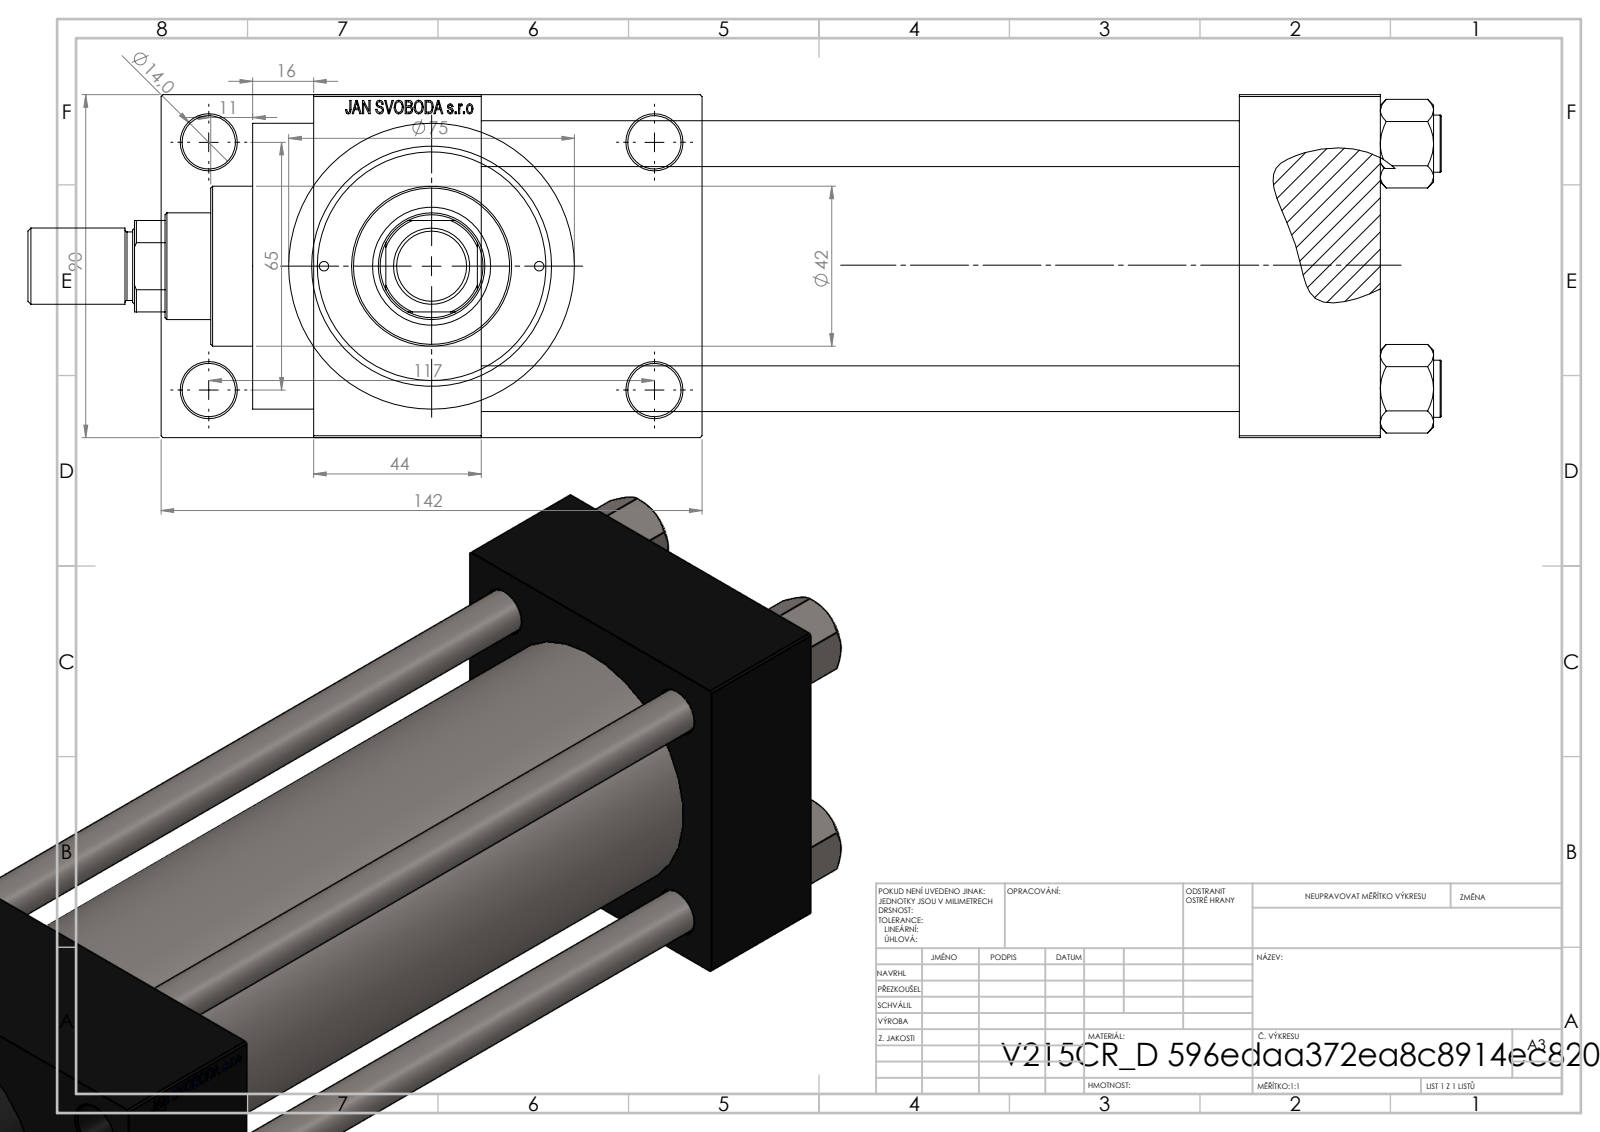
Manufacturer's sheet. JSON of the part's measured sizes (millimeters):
{"part_name": "V215_VC_A; NUT_M5_D; V215CR_VCP_D; V215CR_D_Body (+2 more)", "step_written_by": "SolidWorks 2019 (CONFIG_CONTROL_DESIGN)", "units": "millimeters", "bodies": {"solids": 12, "faces": 1125, "planar": 503, "cylindrical": 96, "other": 526}, "overall_size": [371, 142, 90], "volume_mm3": 1341000, "surface_area_mm2": 294146, "round_holes": [[12, 4], [14, 4], [2.5, 2], [7, 2], [20.96, 2], [30, 2], [18.5, 1], [28, 1], [31, 1], [50, 1], [60, 1], [63, 1]], "round_bosses_or_shafts": [[15, 4], [75, 1], [69, 1], [42, 1], [20, 1], [18, 1]], "partial_cylinders_radius": [[13.5, 1]], "face_to_face_distances": [90, 199, 37, 236, 243, 280, 44, 26, 116, 16], "hole_center_spacings": [26.35, 32.39, 44.4, 45.47, 64.3, 66.92, 68.42, 69.81]}
